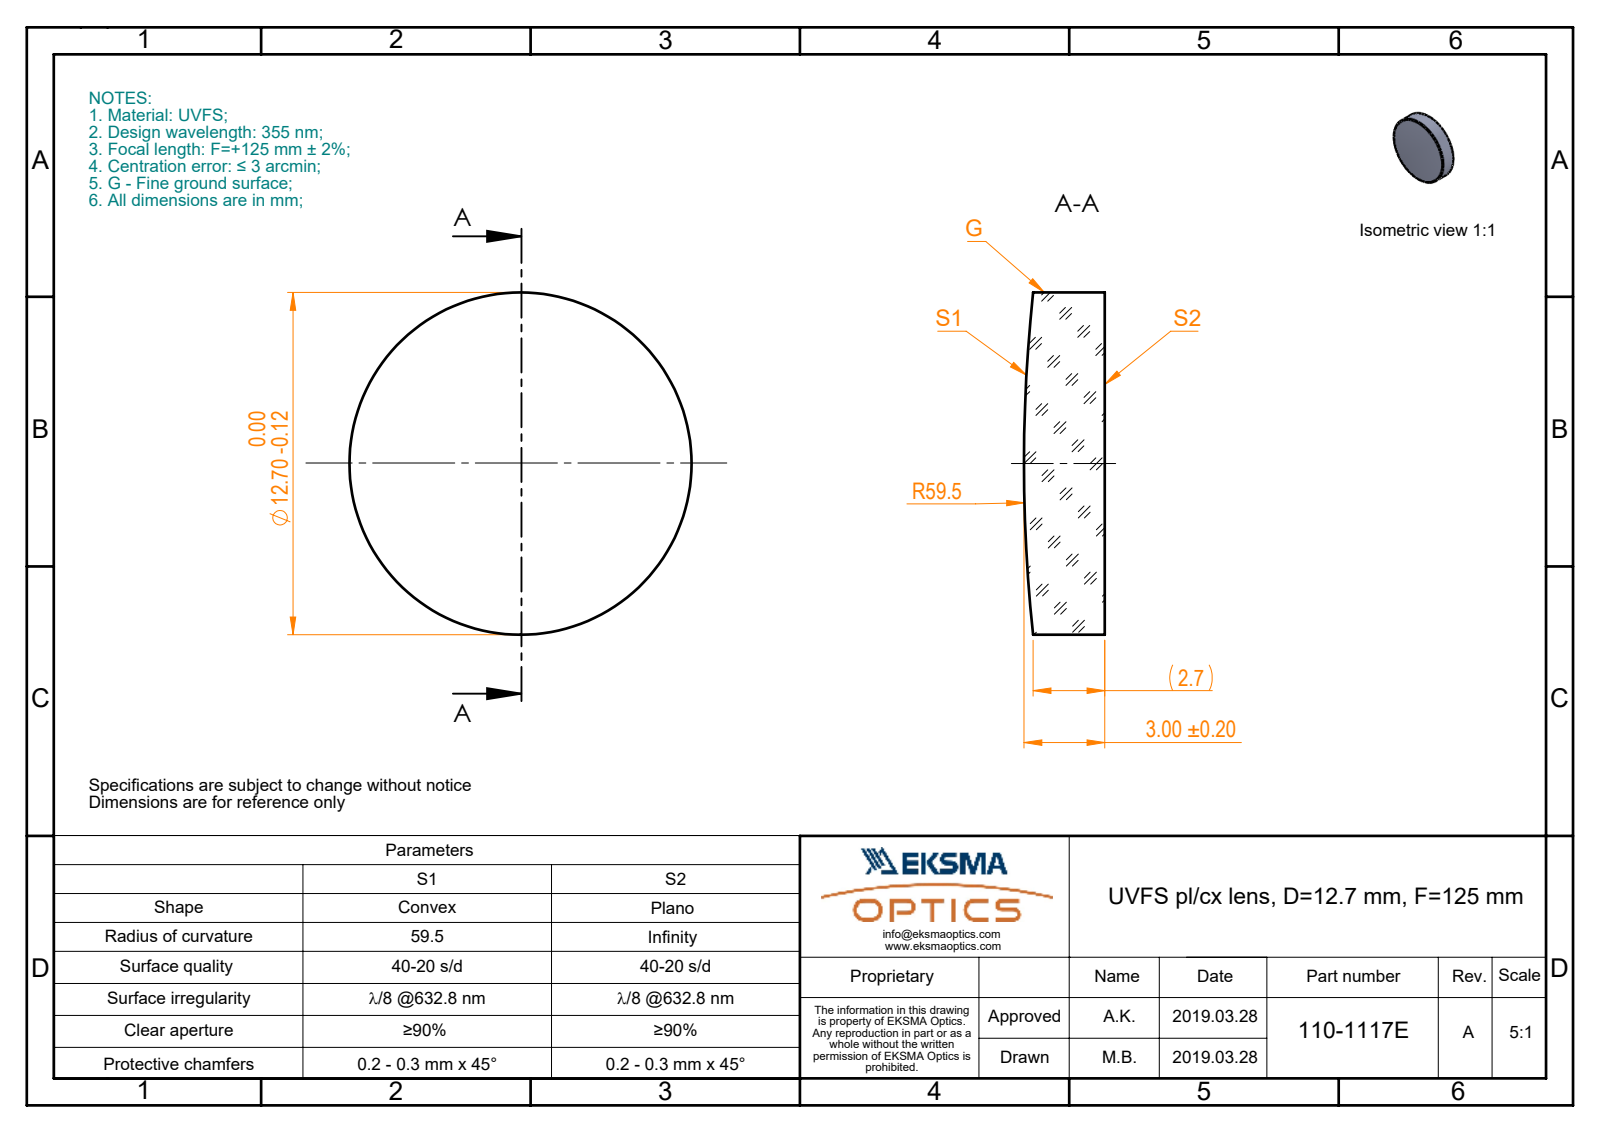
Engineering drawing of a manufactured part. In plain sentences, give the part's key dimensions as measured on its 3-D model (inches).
The part is named "110-1117E UVFS pl-cx 12.7 F125". Its 3-D file was written by "SolidWorks 2017 (CONFIG_CONTROL_DESIGN)". It is 1 solid with 5 faces: 1 planar, 2 cylindrical and 2 other. Overall it measures 0.5 by 0.5 by 0.118 inches. Its volume is 0.022 cubic inches and its surface area 0.558 square inches. Round bosses or shafts: 1 of diameter 0.5.
